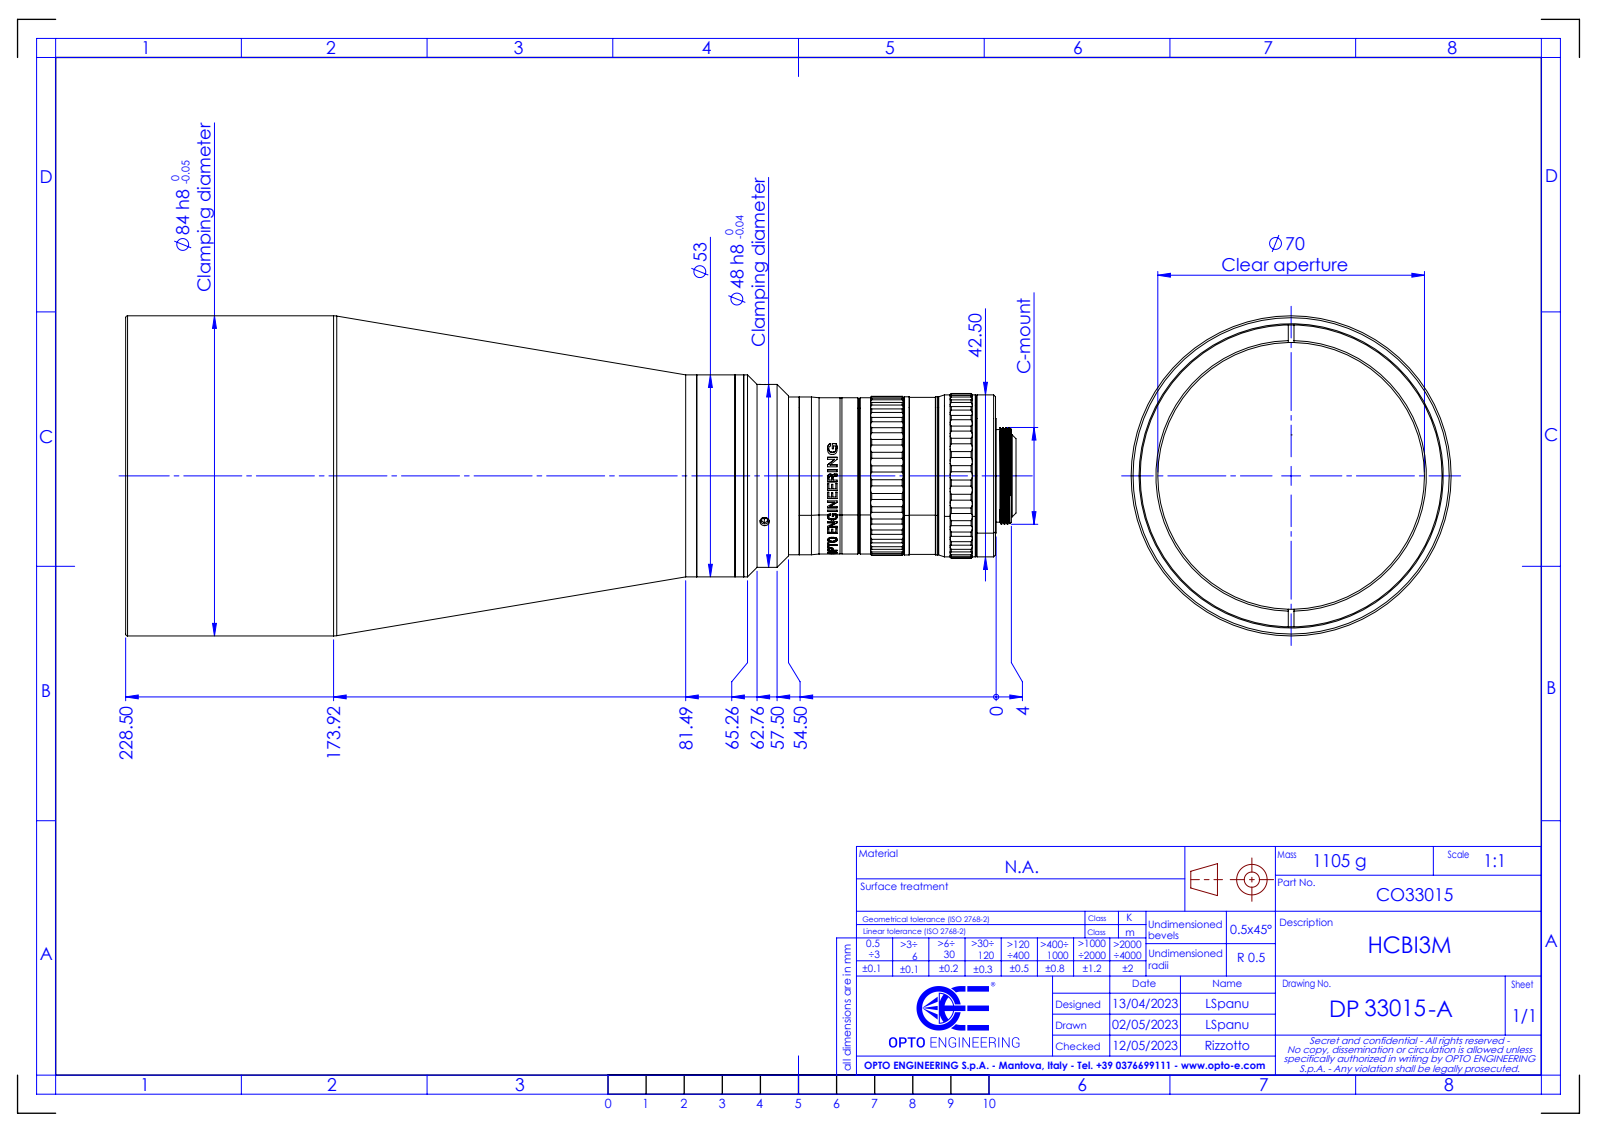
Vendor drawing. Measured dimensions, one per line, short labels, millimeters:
name: DP33015-A_HCBI3M
written by: SolidWorks 2021 (CONFIG_CONTROL_DESIGN)
unit: mm
bodies: 0 solids, 647 faces (104 planar, 363 cylindrical, 180 other)
size: 233.72 × 84 × 84
holes: 3× ⌀2.5, 3× ⌀2.6, 1× ⌀13, 1× ⌀70, 1× ⌀79.25
bosses: 1× ⌀84, 1× ⌀53, 1× ⌀48, 1× ⌀42.5, 1× ⌀41.5, 1× ⌀41.4, 1× ⌀41.2, 1× ⌀41
rounds: 72× R2, 2× R0.75, 2× R2.25, 1× R1, 1× R20.45, 1× R20.55, 1× R20.9, 1× R21.65
face distances: 2.75, 161.73, 158.98, 227.83, 225.08, 66.1, 159.5, 156.75, 2.23, 68.33
hole spacings: 17.5, 30.3, 17.49, 30.31
